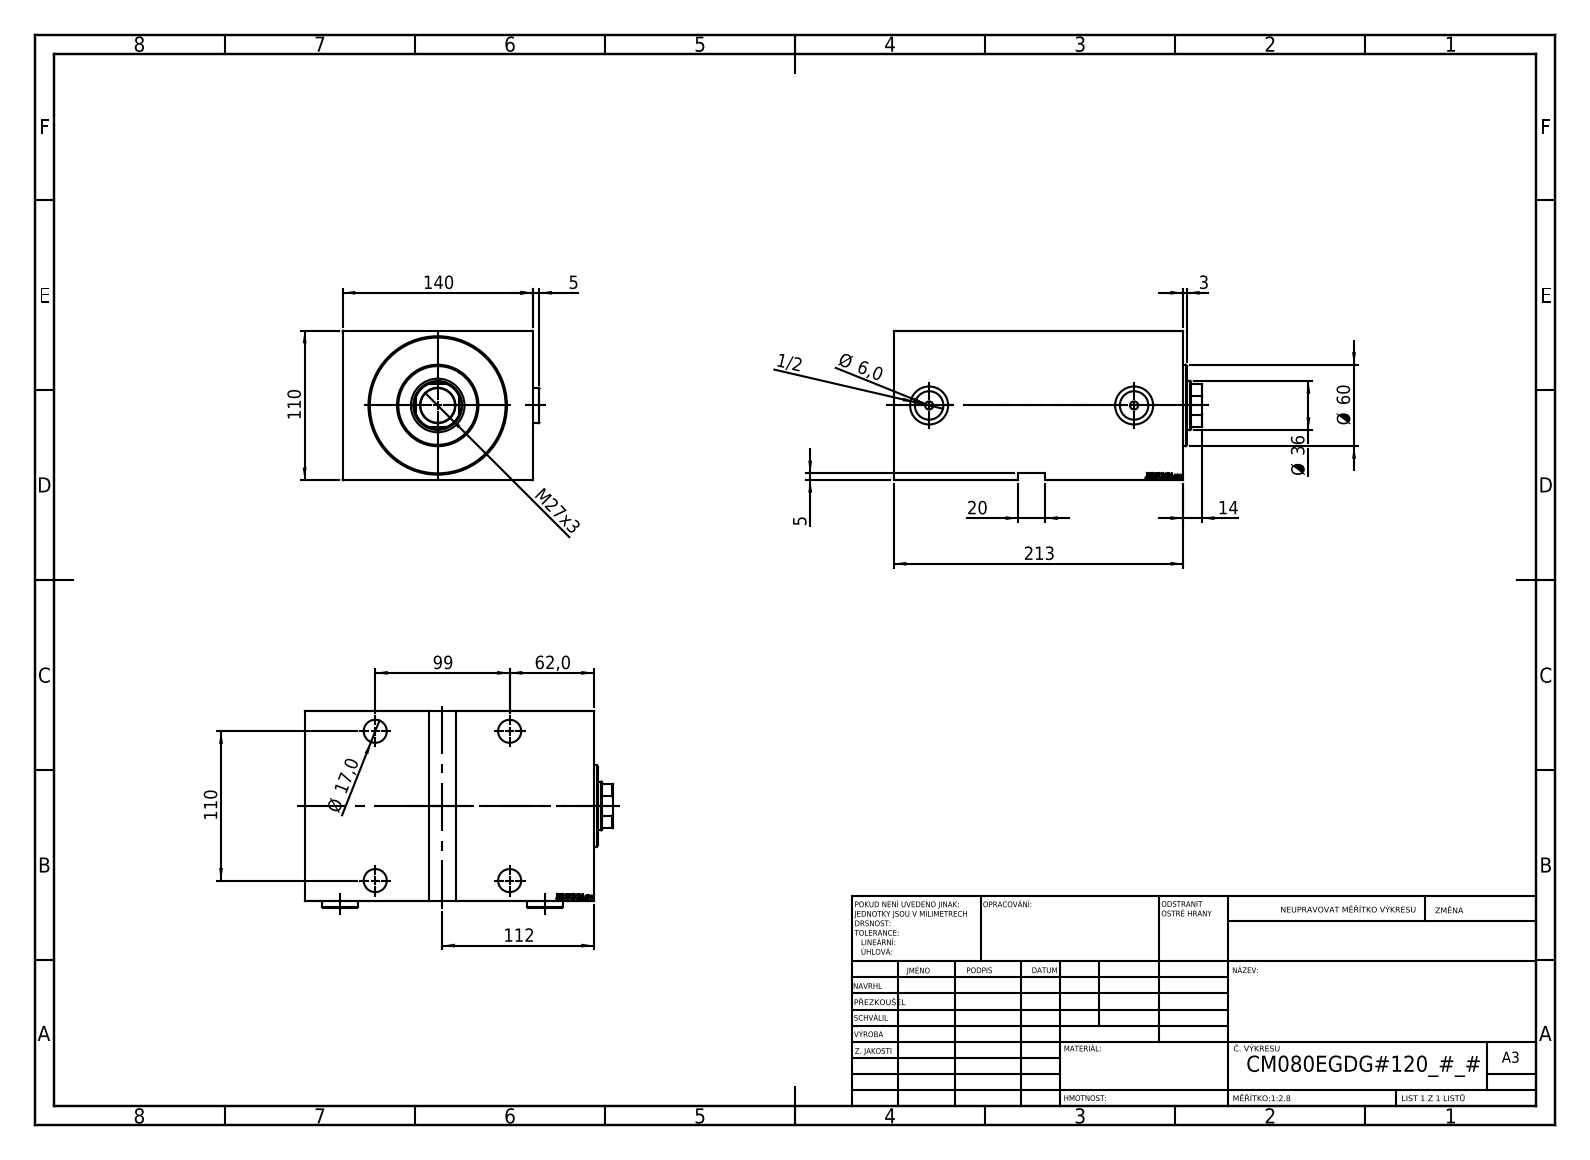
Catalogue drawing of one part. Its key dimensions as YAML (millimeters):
part_name: "V450CM_E_VCP; V450CM_E_Body; Zatka_OIL_PORT; V450CM_VC_B"
step_written_by: "SolidWorks 2019 (CONFIG_CONTROL_DESIGN)"
units: millimeters
bodies: {solids: 5, faces: 912, planar: 446, cylindrical: 68, other: 398}
overall_size: [227, 144.9, 110]
volume: 2657000
surface_area: 283364
round_holes:
  - {diameter: 17, count: 4}
  - {diameter: 25, count: 4}
  - {diameter: 6, count: 2}
  - {diameter: 20.96, count: 2}
  - {diameter: 28, count: 2}
  - {diameter: 25.5, count: 1}
  - {diameter: 36, count: 1}
  - {diameter: 39.5, count: 1}
  - {diameter: 80, count: 1}
  - {diameter: 100, count: 1}
round_bosses_or_shafts:
  - {diameter: 26, count: 2}
  - {diameter: 82, count: 1}
  - {diameter: 60, count: 1}
partial_cylinders:
  - {radius: 17.5, count: 1}
face_to_face_distances: [110, 140, 213, 21, 192, 5, 208, 187, 79, 196.4]
hole_center_spacings: [99, 110, 147.99, 151]
